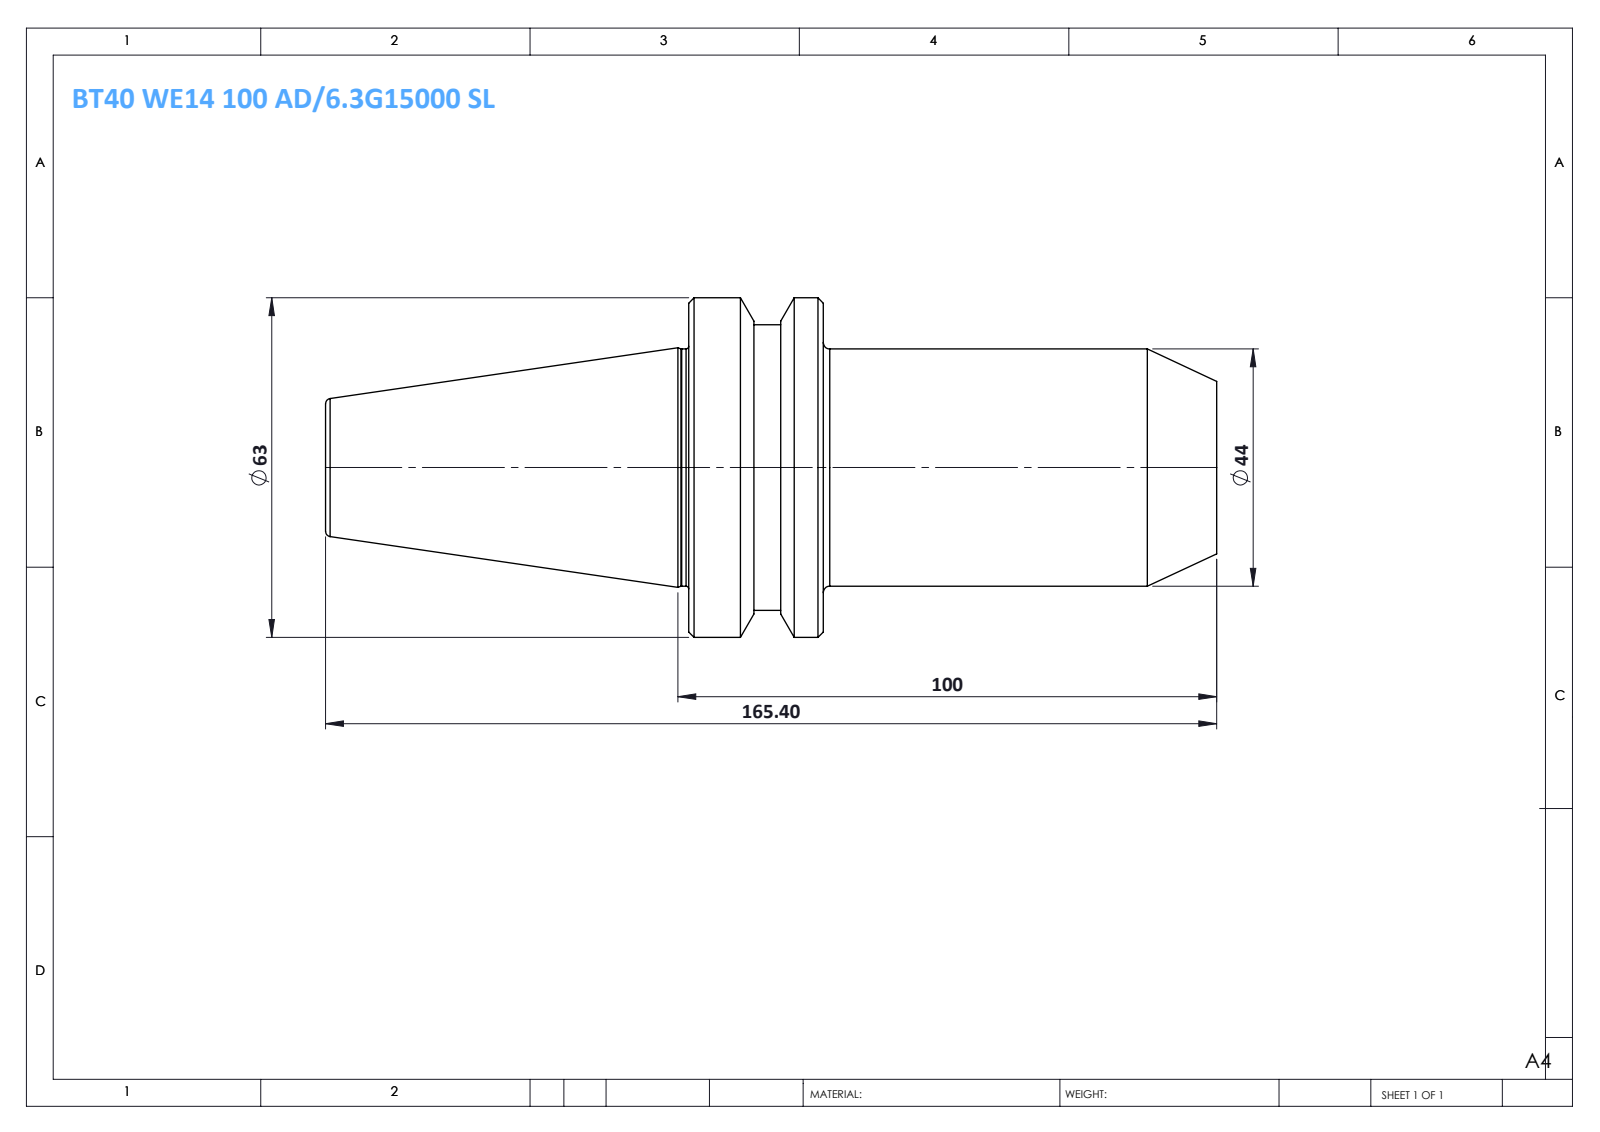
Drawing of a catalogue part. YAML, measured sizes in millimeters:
part_name: "BT40 WE14 100 AD-6.3G15000 SL"
step_written_by: "SolidWorks 2014 (CONFIG_CONTROL_DESIGN)"
units: millimeters
bodies: {solids: 1, faces: 38, planar: 6, cylindrical: 10, other: 22}
overall_size: [165.4, 63, 63]
volume: 244538
surface_area: 27553
round_bosses_or_shafts:
  - {diameter: 63, count: 1}
  - {diameter: 53, count: 1}
  - {diameter: 44, count: 1}
face_to_face_distances: [25, 73, 98, 165.4, 92.4, 67.4, 85.9, 12.9, 12.1, 79.5]
